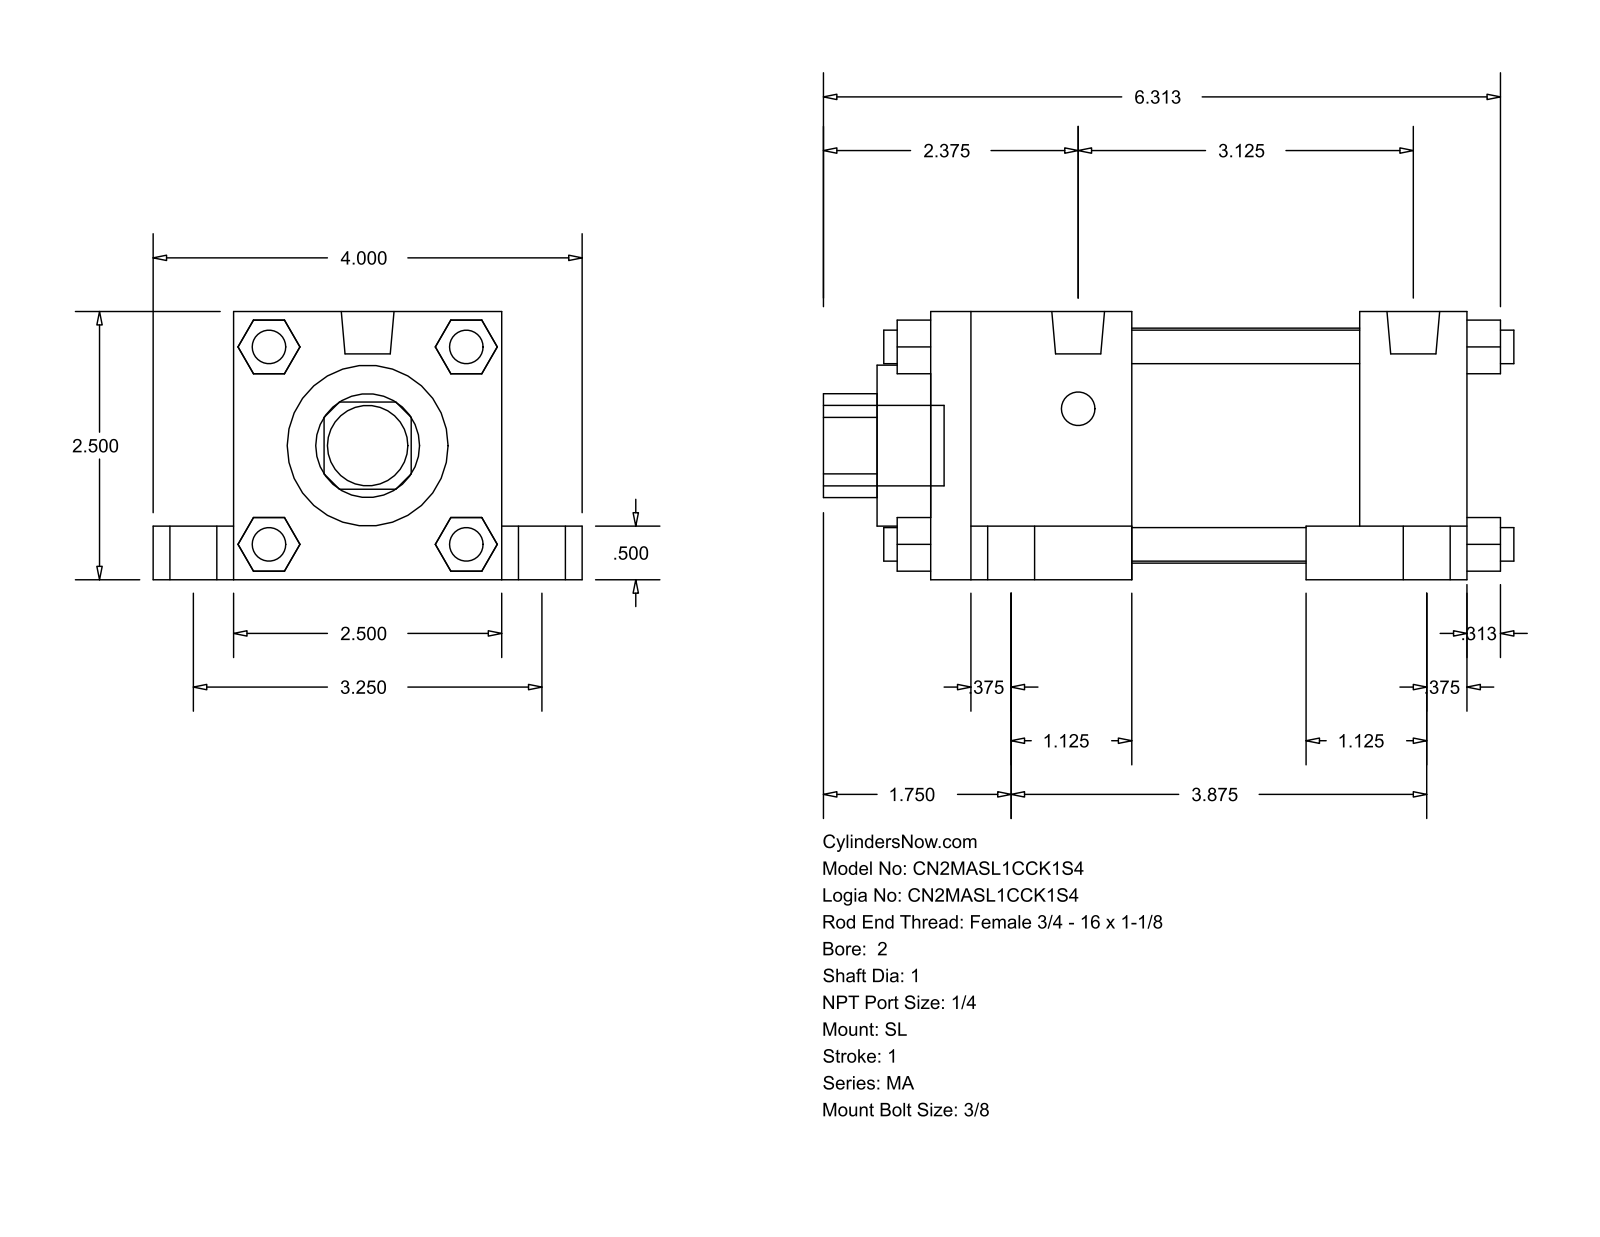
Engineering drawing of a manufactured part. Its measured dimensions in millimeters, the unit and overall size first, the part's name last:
Units: millimetres
Overall size (bounding box): 163.51 × 101.6 × 63.5
Round holes (diameter × count): ⌀25.4 ×1, ⌀38.1 ×1, ⌀55.63 ×1
Round bosses / shafts (diameter × count): ⌀7.94 ×8, ⌀17.46 ×4, ⌀11.11 ×4, ⌀12.49 ×2, ⌀19.05 ×1
Partial cylindrical surfaces — rounded edges, fillets, slot ends (radius × count): R12.29 ×1
Main face-to-face distances: 63.5, 12.7, 127, 101.6, 19.05, 82.55, 25.4, 50.8, 47.63, 79.37
Bodies: 0 solids, 148 faces (112 planar, 36 cylindrical, 0 other)
Part name (STEP PRODUCT): MA_SL__0200_1
STEP written by: GSSL Pune (CONFIG_CONTROL_DESIGN)
